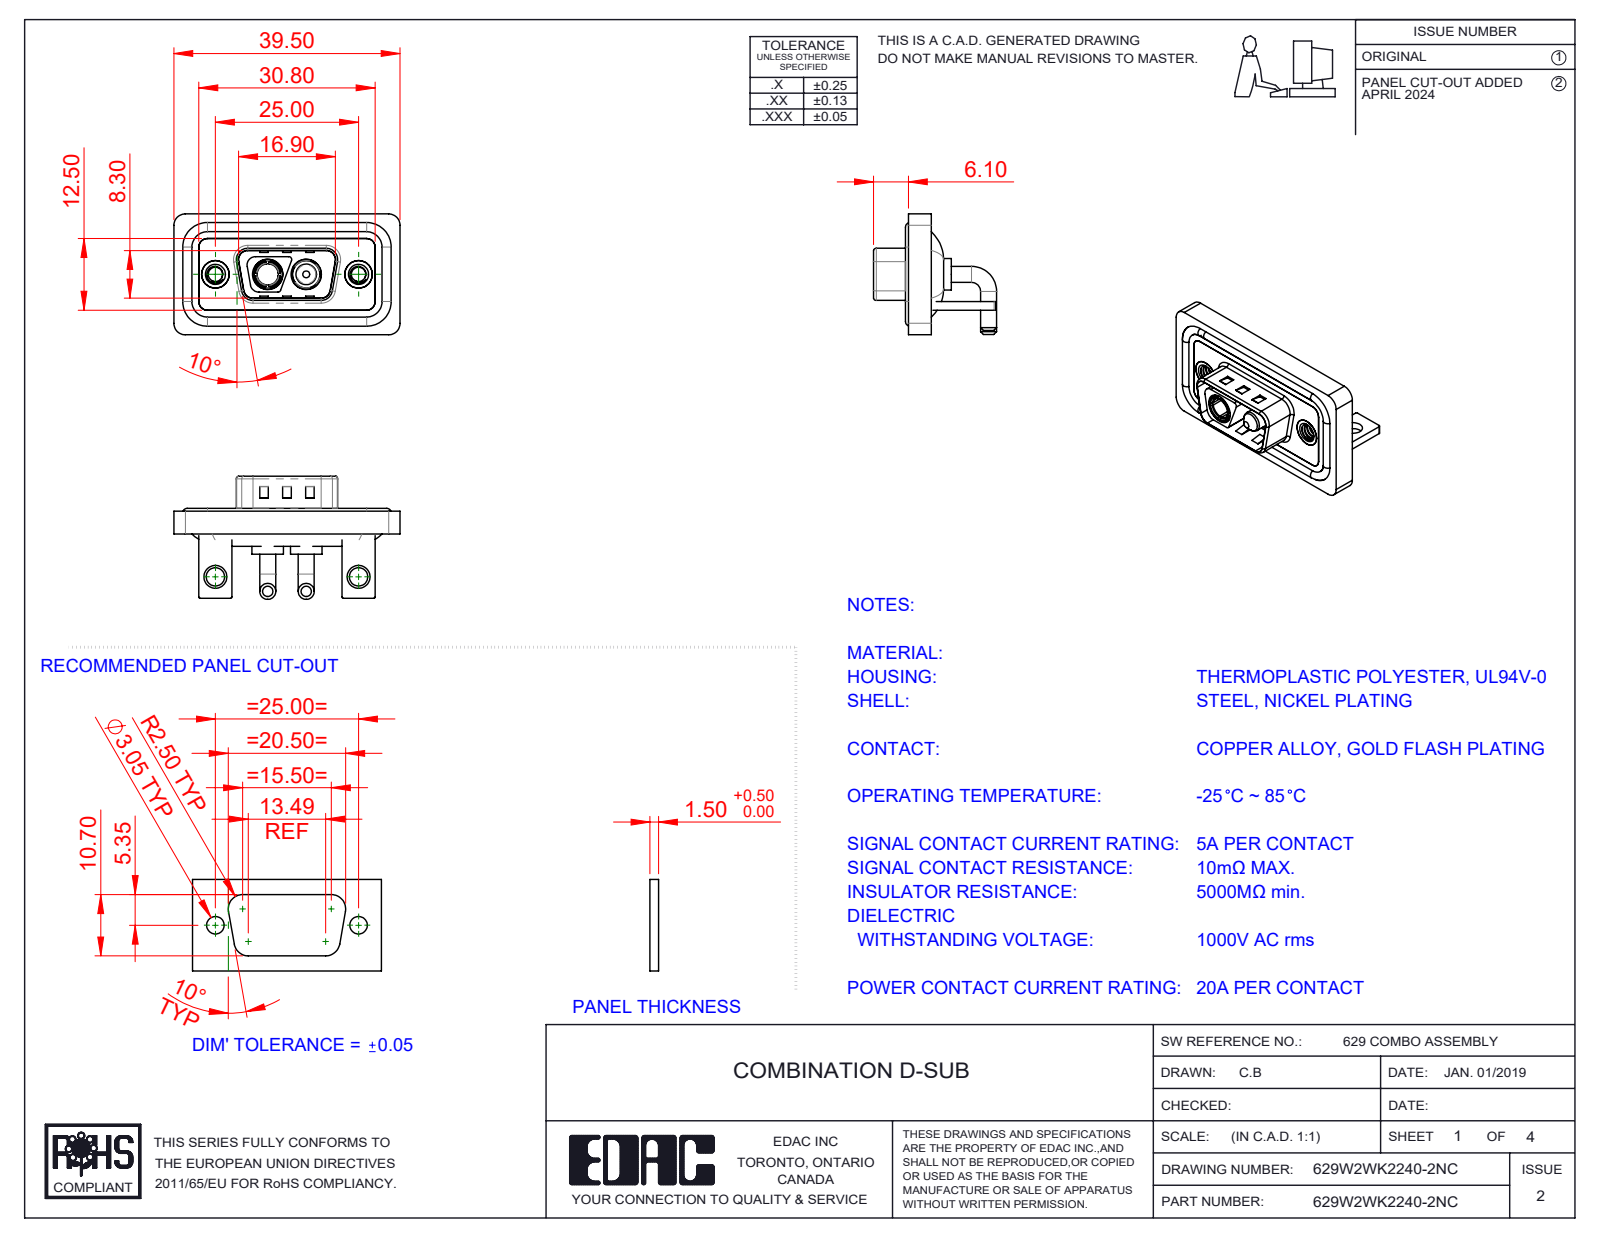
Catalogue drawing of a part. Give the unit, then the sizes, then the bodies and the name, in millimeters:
Units: millimetres
Overall size (bounding box): 39.5 × 21.5 × 21.1
Round holes (diameter × count): ⌀2.5 ×2, ⌀3.2 ×2, ⌀4 ×2, ⌀4.8 ×2, ⌀4.85 ×2, ⌀5 ×2, ⌀5.3 ×2, ⌀3.7 ×1
Round bosses / shafts (diameter × count): ⌀2.8 ×4, ⌀1.6 ×4, ⌀5.5 ×2, ⌀5.2 ×2, ⌀4.9 ×2, ⌀4.75 ×2, ⌀3.75 ×2, ⌀4.96 ×1
Partial cylindrical surfaces — rounded edges, fillets, slot ends (radius × count): R1.5 ×20, R2 ×19, R0.25 ×16, R0.5 ×11, R1.6 ×8, R0.6 ×4, R0.65 ×4, R0.9 ×4
Main face-to-face distances: 0.4, 1.5, 2.9, 0.8, 1.1, 1.2, 2.1, 1.6, 3.7, 2.5
Hole centre spacings: 9.14, 15.86, 25, 6.72
Volume: 4 954 mm³ · Surface area: 8 120 mm²
Bodies: 13 solids, 580 faces (209 planar, 249 cylindrical, 122 other)
Part name (STEP PRODUCT): 629Combo Waterproof Housing_09 Contacts; Power Socket_20A RA; 629Combo Stabilizer Bracket; 629Combo Housing_2WK2 (+5 more)
STEP written by: SolidWorks 2023 (CONFIG_CONTROL_DESIGN)
